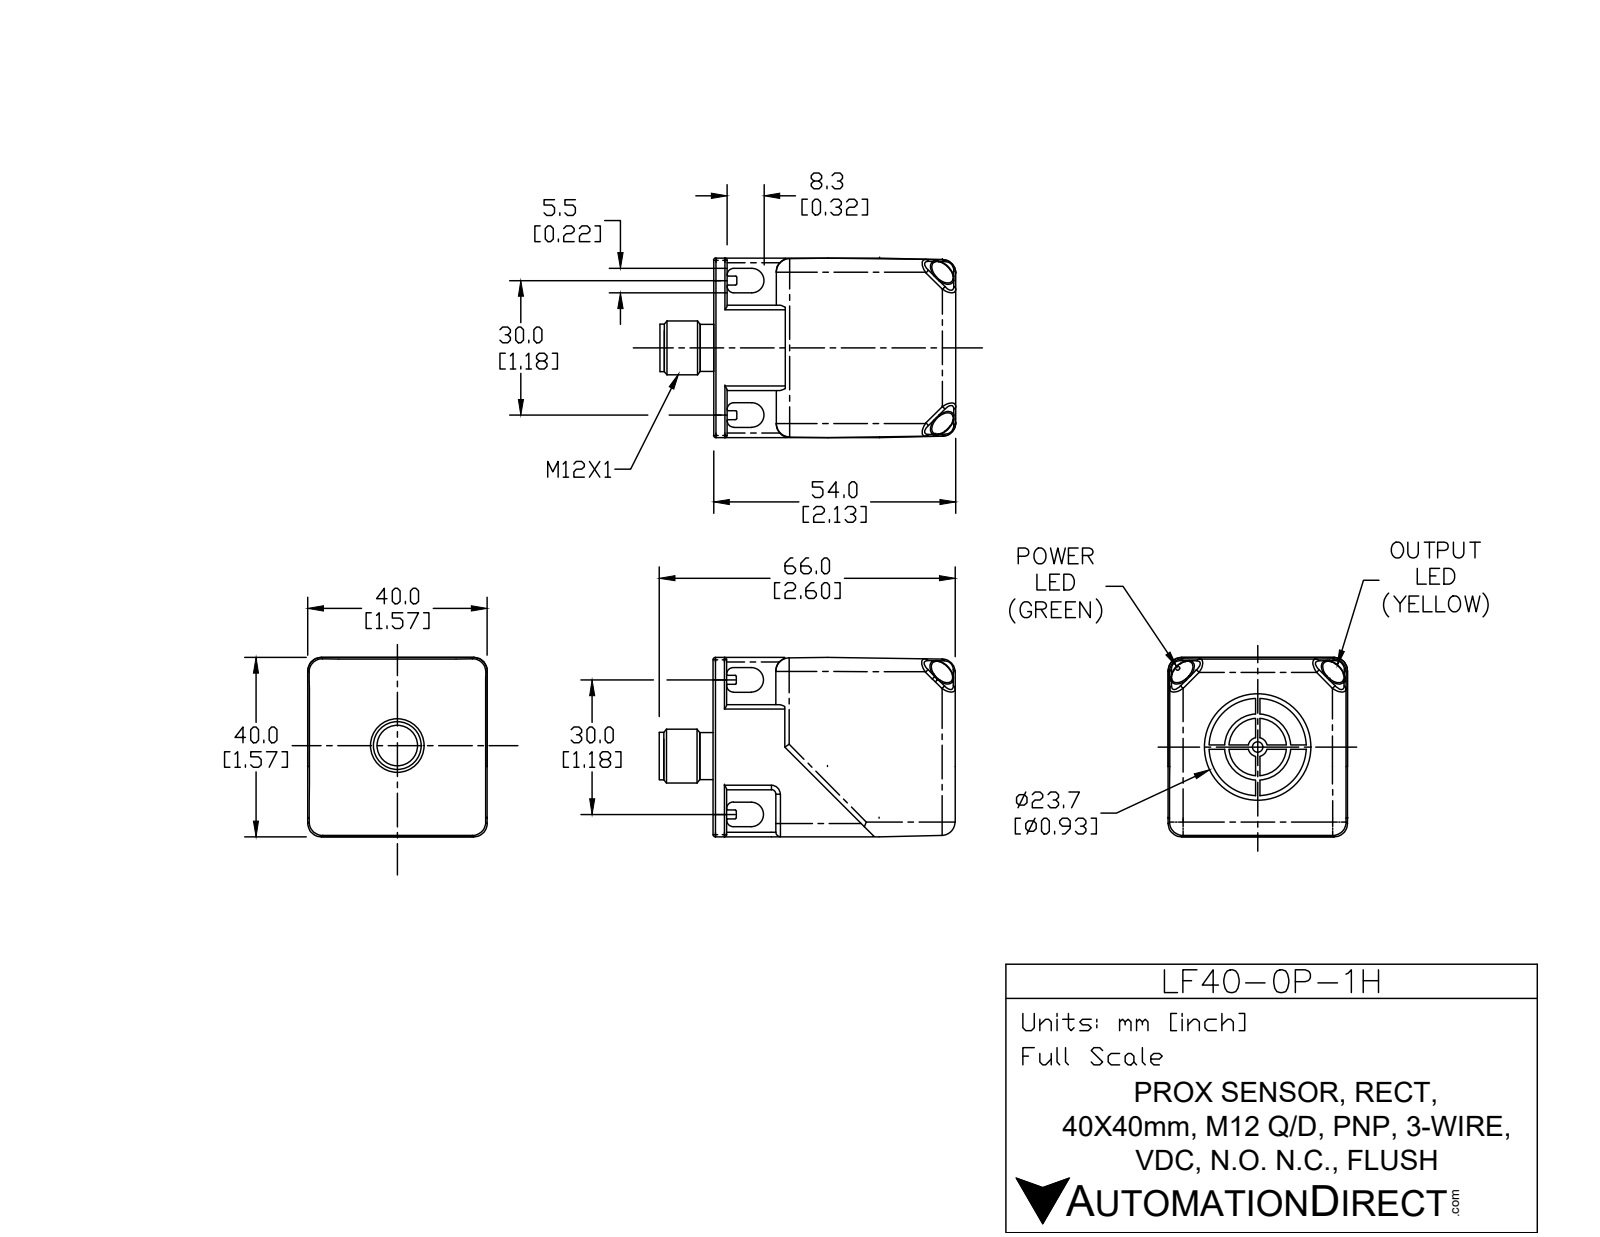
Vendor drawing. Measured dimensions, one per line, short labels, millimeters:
name: LF40-0P-1H
written by: SolidWorks 2017 (AUTOMOTIVE_DESIGN)
unit: mm
bodies: 1 solid, 222 faces (110 planar, 99 cylindrical, 13 other)
size: 66 × 40 × 40
volume: 78 080 mm³; area: 15 060 mm²
holes: 1× ⌀8.4, 1× ⌀9.2, 1× ⌀14.8, 1× ⌀23.7
bosses: 1× ⌀21.7, 1× ⌀12.8, 1× ⌀12, 1× ⌀10.6, 1× ⌀10.5, 1× ⌀9, 1× ⌀7, 1× ⌀2.3
rounds: 16× R0.2, 10× R1, 10× R3, 8× R1.5, 4× R0.5, 4× R2.7, 4× R5, 1× R0.6
face distances: 40, 54, 10.5, 29.5, 30, 3, 51, 8.3, 2.3, 7.7
hole spacings: 2
